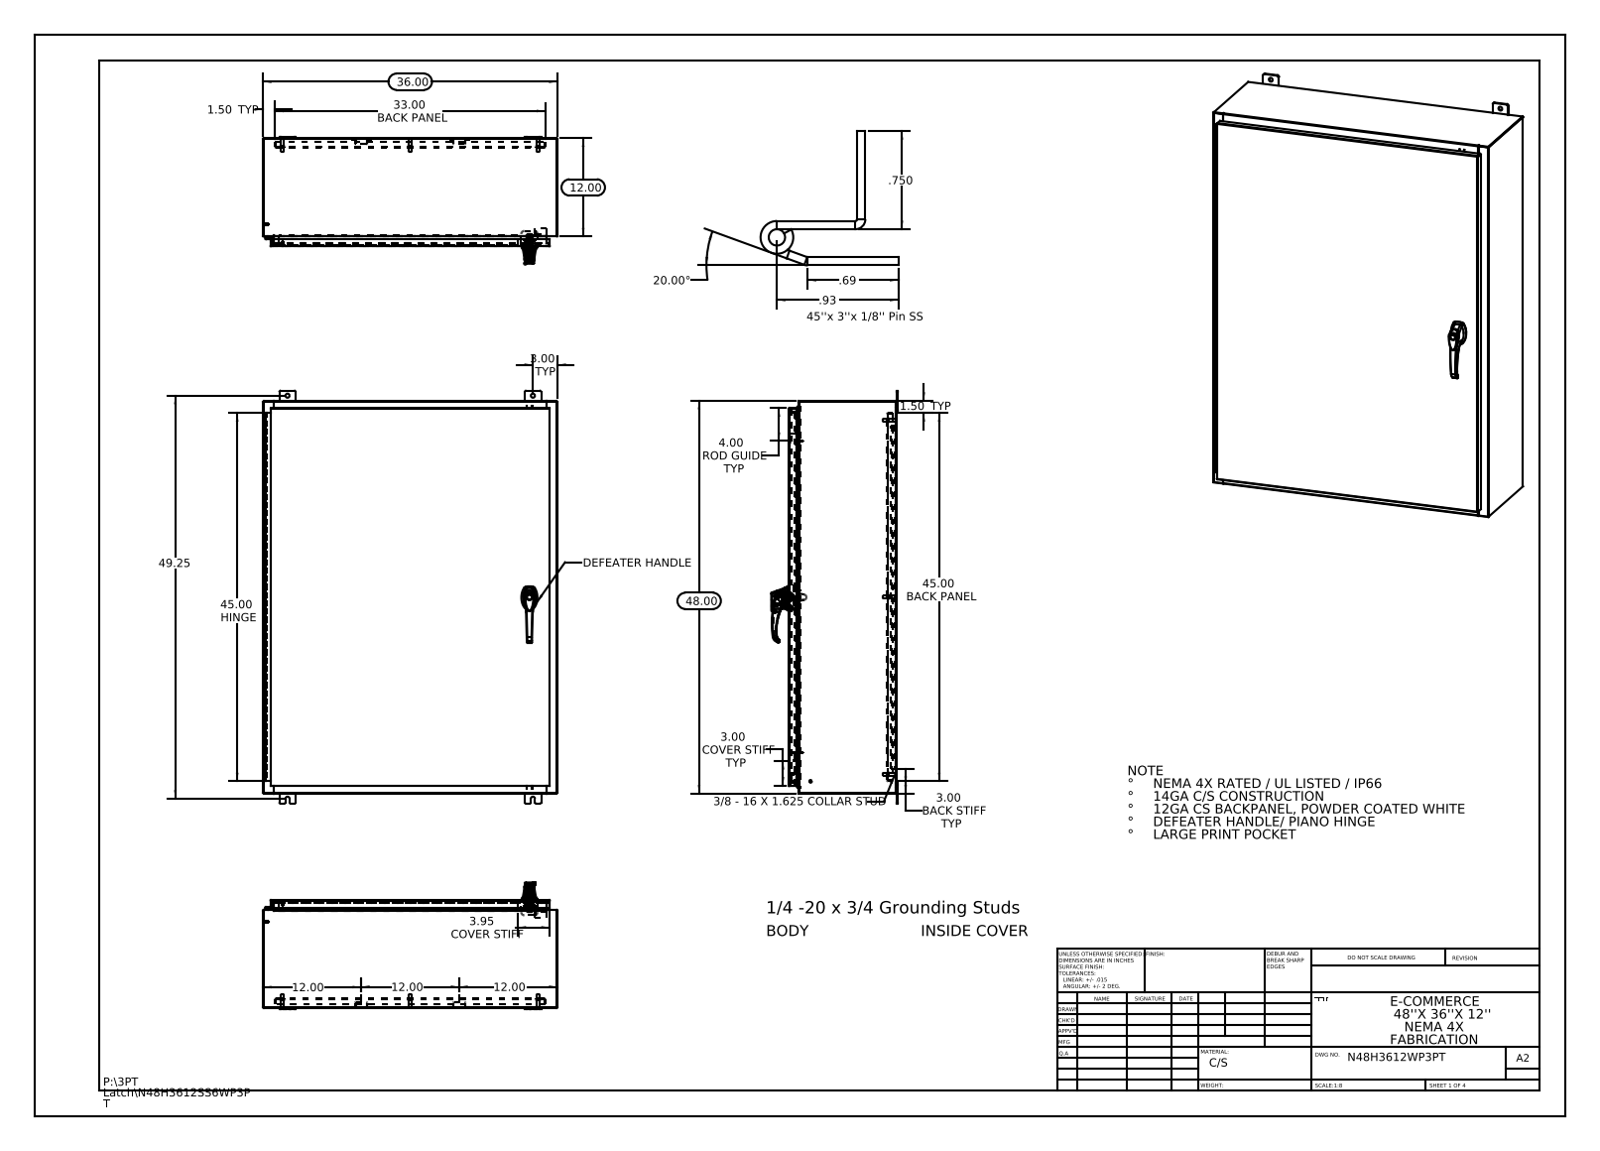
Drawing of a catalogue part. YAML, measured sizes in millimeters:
part_name: "26161102; 00005310_26163101; N48H3612SS6WP3PT Mounting Studs; Quarter-20 CD Stud (+8 more)"
step_written_by: "SolidWorks 2013 (CONFIG_CONTROL_DESIGN)"
units: millimeters
bodies: {solids: 51, faces: 3400, planar: 1309, cylindrical: 1305, other: 786}
overall_size: [1282.7, 914.4, 393.6]
volume: 10750000
surface_area: 10520000
round_holes:
  - {diameter: 12.7, count: 12}
  - {diameter: 6.4, count: 10}
  - {diameter: 3.5, count: 3}
  - {diameter: 4.1, count: 3}
  - {diameter: 2, count: 2}
  - {diameter: 5.2, count: 2}
  - {diameter: 8, count: 2}
  - {diameter: 11.1, count: 2}
  - {diameter: 3.2, count: 1}
  - {diameter: 3.2, count: 1}
  - {diameter: 5, count: 1}
  - {diameter: 7, count: 1}
round_bosses_or_shafts:
  - {diameter: 4, count: 10}
  - {diameter: 3.6, count: 10}
  - {diameter: 15.9, count: 8}
  - {diameter: 9.5, count: 8}
  - {diameter: 8.4, count: 8}
  - {diameter: 8, count: 3}
  - {diameter: 6, count: 3}
  - {diameter: 30, count: 1}
partial_cylinders:
  - {radius: 3, count: 37}
  - {radius: 0.3, count: 34}
  - {radius: 0.2, count: 33}
  - {radius: 2.2, count: 28}
  - {radius: 4.8, count: 24}
  - {radius: 1, count: 15}
  - {radius: 0.7, count: 12}
  - {radius: 0.2, count: 6}
face_to_face_distances: [1.9, 333.4, 331.5, 335.3, 2.6, 25.4, 308, 27.3, 306.1, 29.9]
hole_center_spacings: [440.9, 499.5, 549.3, 965.3, 1168, 793.8, 1098.6, 7.5]
